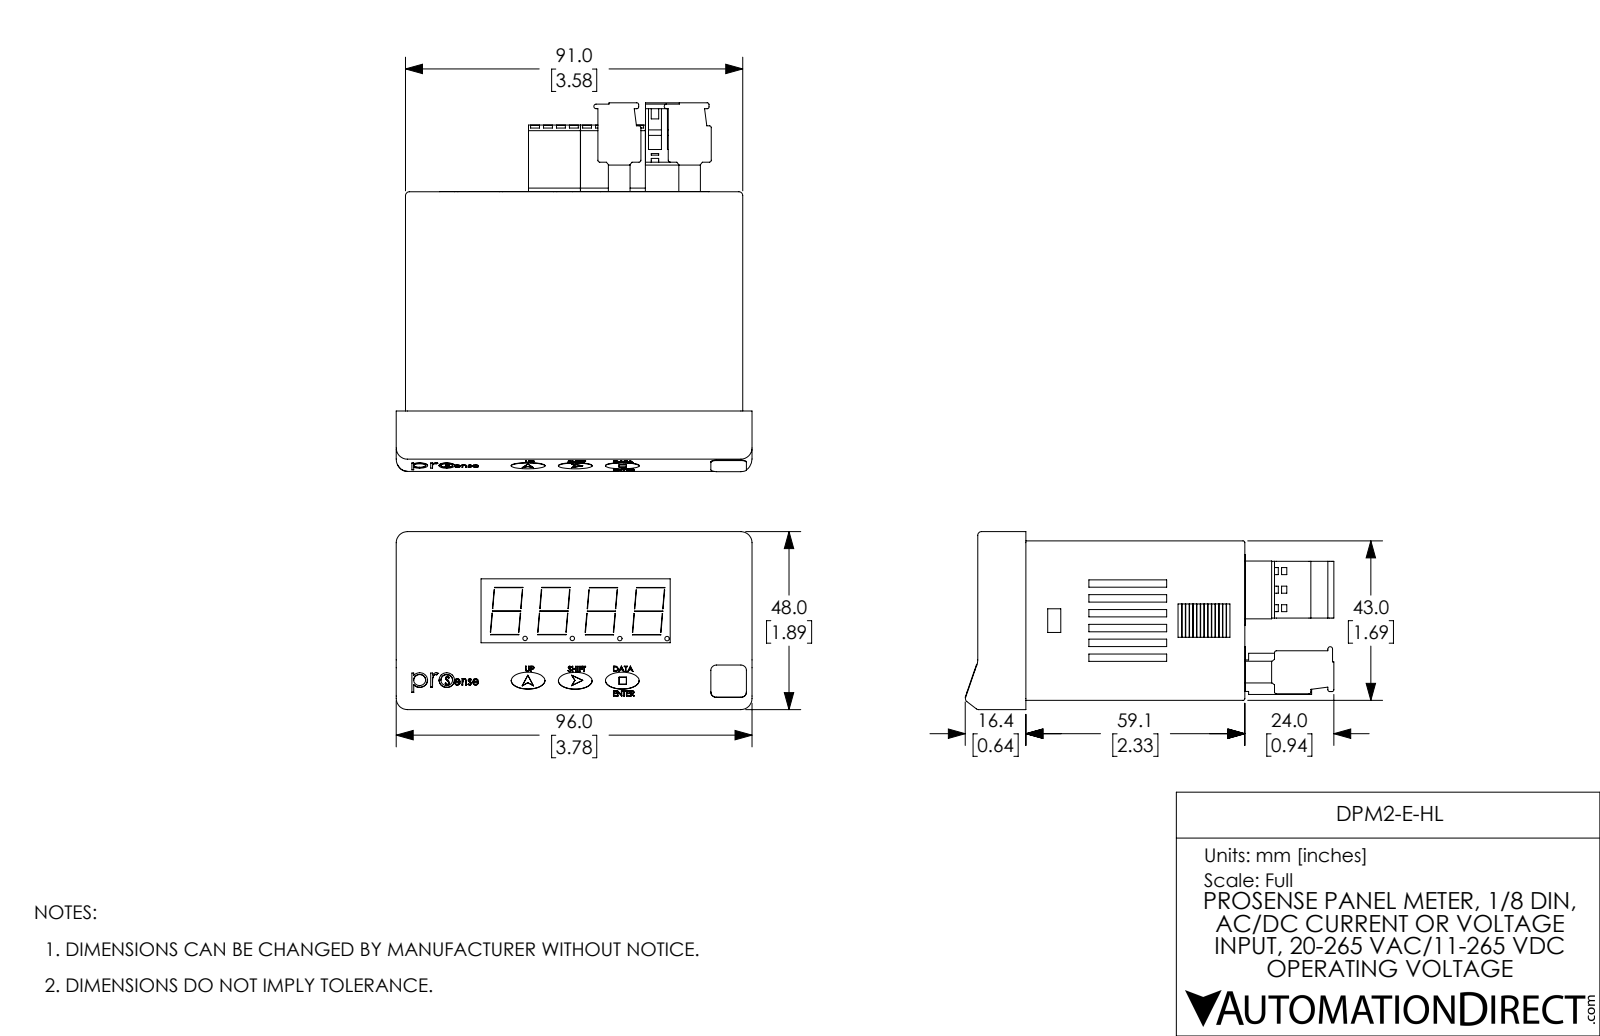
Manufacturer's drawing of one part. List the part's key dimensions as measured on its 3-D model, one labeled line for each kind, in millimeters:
Part name (STEP PRODUCT): DPM2-E-HL
STEP written by: SolidWorks 2017 (AUTOMOTIVE_DESIGN)
Units: millimetres
Bodies: 10 solids, 1936 faces (1502 planar, 278 cylindrical, 156 other)
Overall size (bounding box): 99.5 × 96 × 48
Volume: 88 360 mm³ · Surface area: 64 370 mm²
Round holes (diameter × count): ⌀1 ×9, ⌀2 ×9, ⌀2 ×8, ⌀3 ×8, ⌀3.9 ×8
Round bosses / shafts (diameter × count): ⌀1.2 ×4
Partial cylindrical surfaces — rounded edges, fillets, slot ends (radius × count): R0.1 ×53, R0.3 ×18, R0.4 ×18, R0.5 ×17, R3 ×10, R1 ×9, R1.8 ×9, R1.8 ×9
Main face-to-face distances: 1.5, 41.5, 2.5, 43, 40, 44, 89.5, 11, 4, 70.6
Hole centre spacings: 3.5, 19, 5, 5, 5.1, 5.1, 7, 19.7
